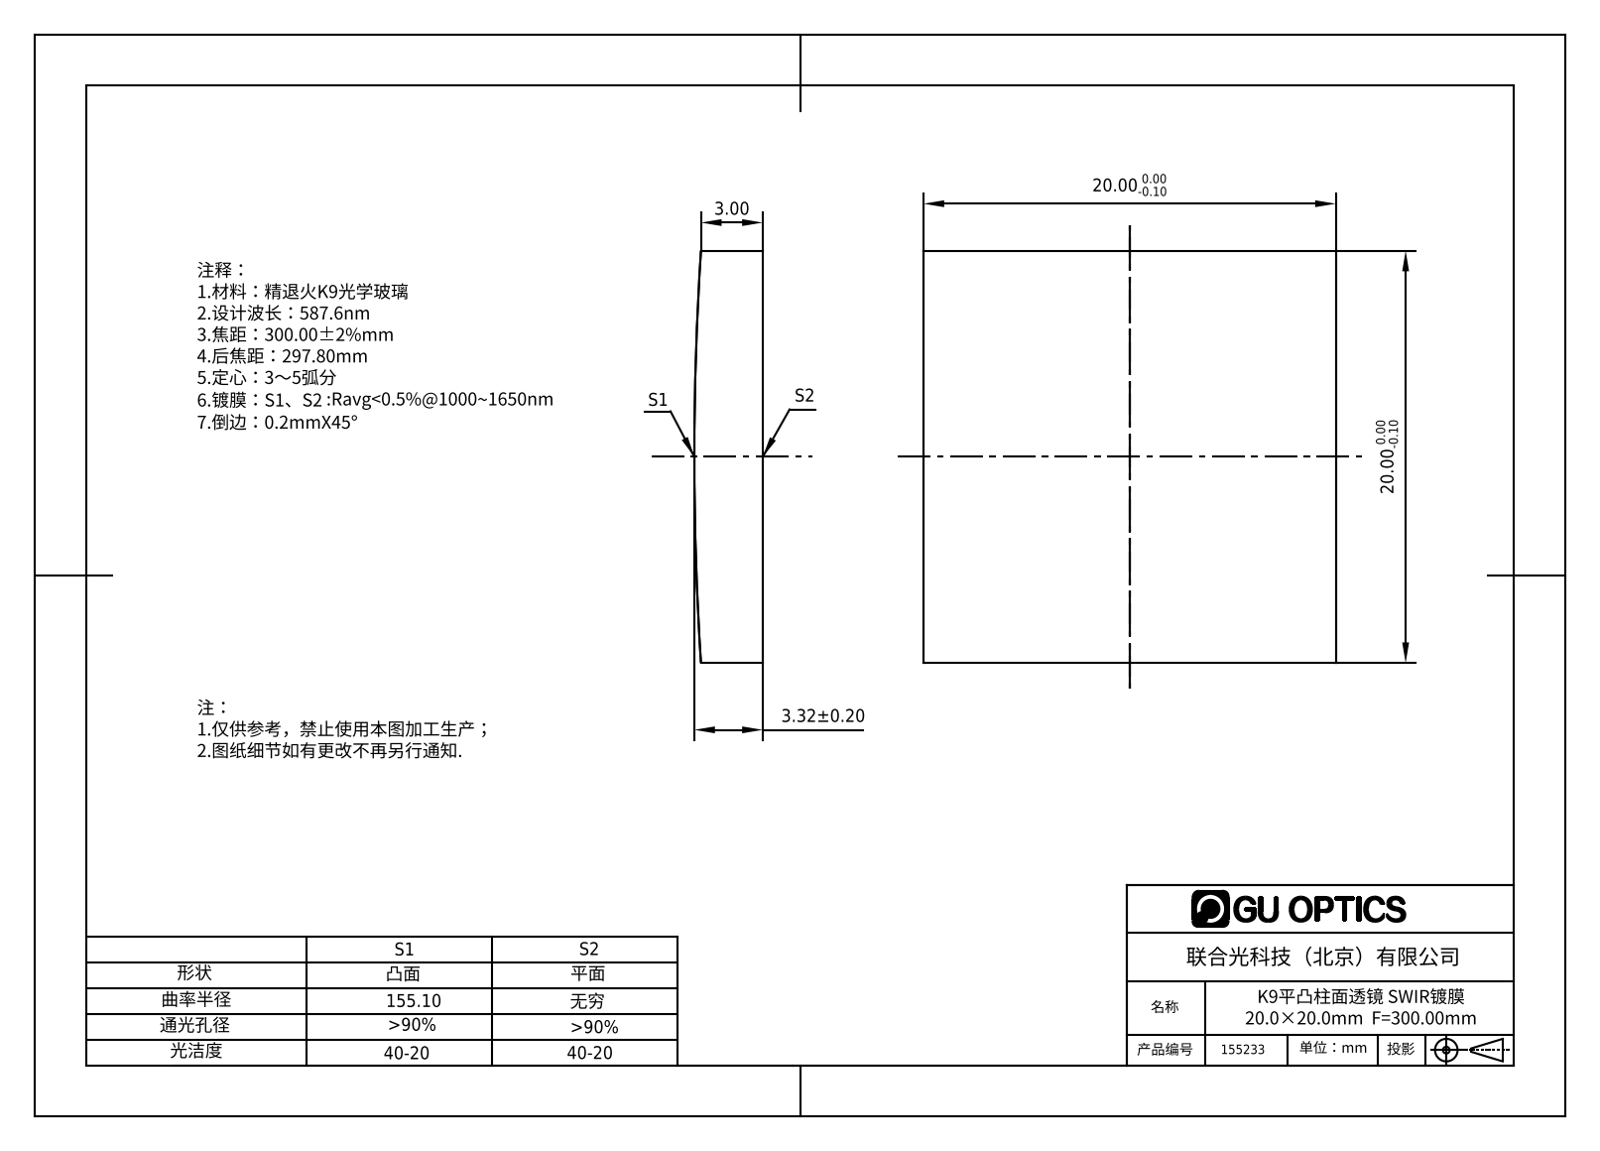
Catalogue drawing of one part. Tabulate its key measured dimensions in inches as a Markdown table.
| quantity | value |
| --- | --- |
| part name | 155035 |
| STEP written by | SolidWorks 2016 (AUTOMOTIVE_DESIGN) |
| units | inches |
| bodies | 1 solid, 6 faces (5 planar, 1 cylindrical, 0 other) |
| overall size | 0.787 × 0.787 × 0.131 |
| volume | 0.078 in³ |
| surface area | 1.626 in² |
| partial cylindrical surfaces (radius × count) | 6.106 × 1 |
| main face-to-face distances | 0.787 |
